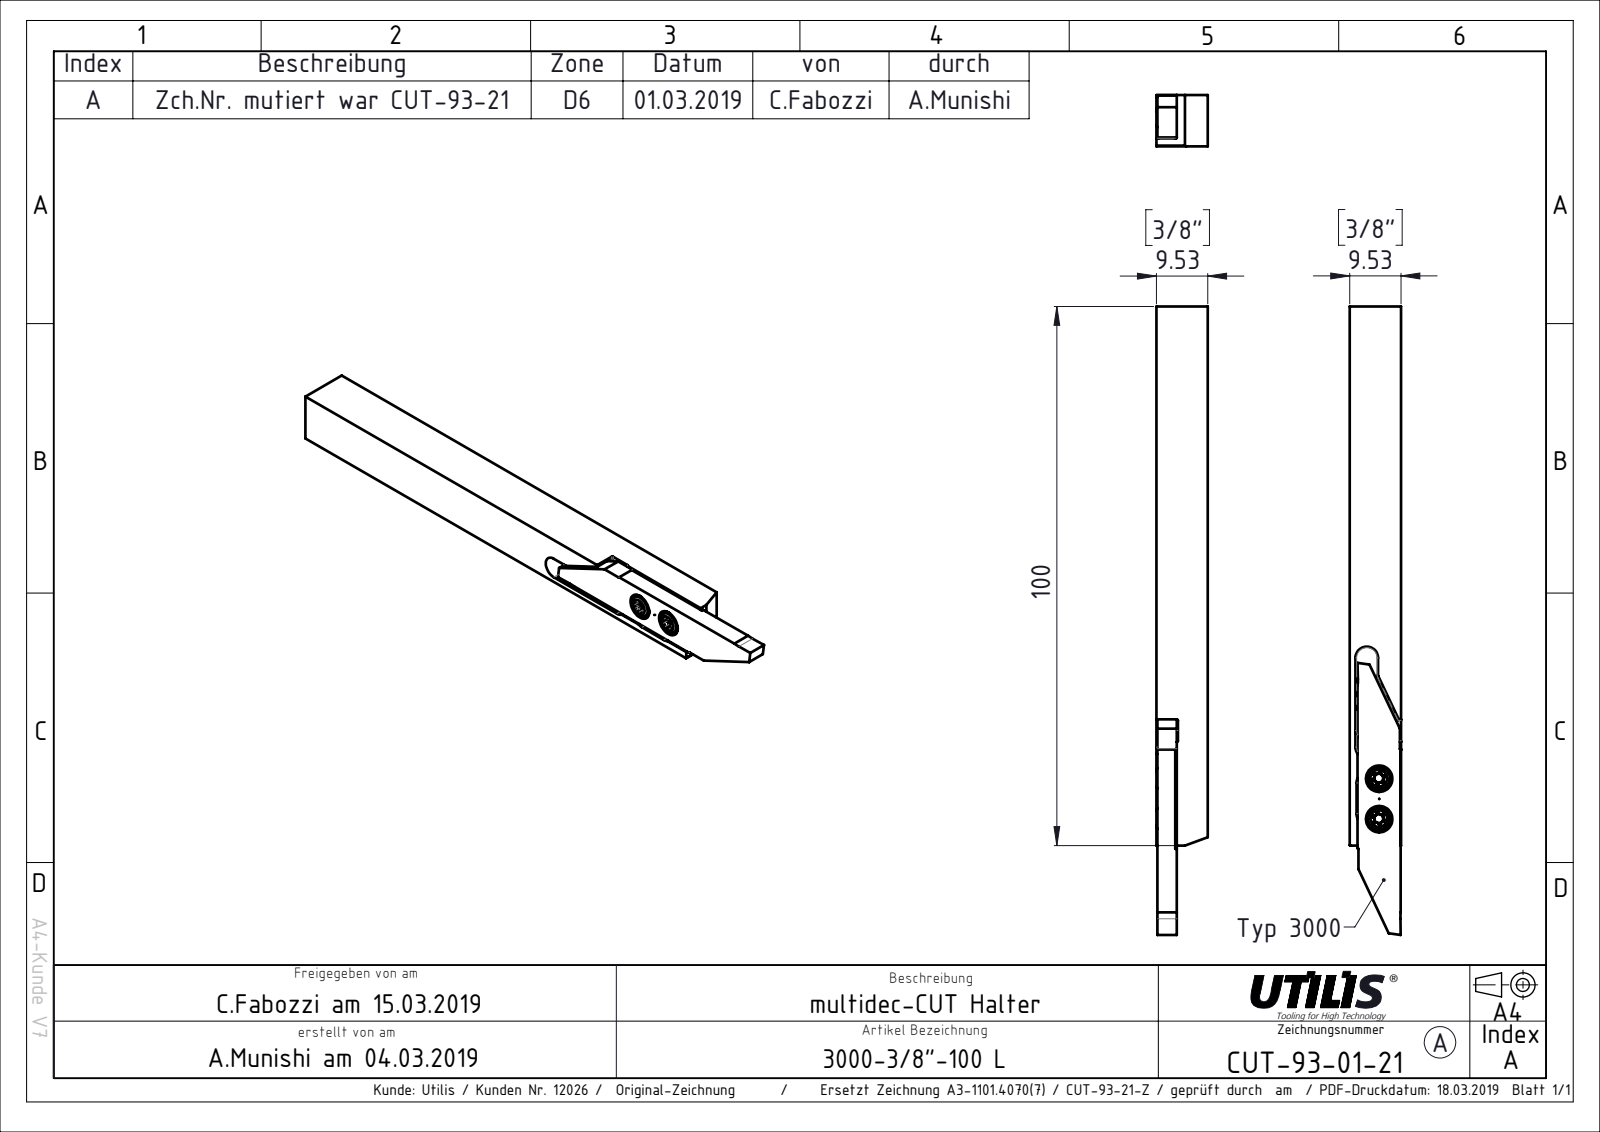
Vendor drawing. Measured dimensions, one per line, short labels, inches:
name: CUT-93-Kunde; CUT-93-21; CUT-Vorlage 3000 R+L Lang Kunde_L-Lang; CUT-Vorlage 3000 R+L Lang Kunde (+1 more)
written by: SolidWorks 2015 (CONFIG_CONTROL_DESIGN)
unit: in
bodies: 2 solids, 55 faces (36 planar, 19 cylindrical, 0 other)
size: 4.587 × 0.375 × 0.375
volume: 0.552 in³; area: 8.065 in²
holes: 2× ⌀0.098, 2× ⌀0.193
rounds: 4× R0.083, 2× R0.006, 2× R0.394
face distances: 0.375, 0.15, 0.226, 0.142, 0.367, 0.06, 0.315, 0.043, 0.018, 0.333
hole spacings: 0.148, 0.295
